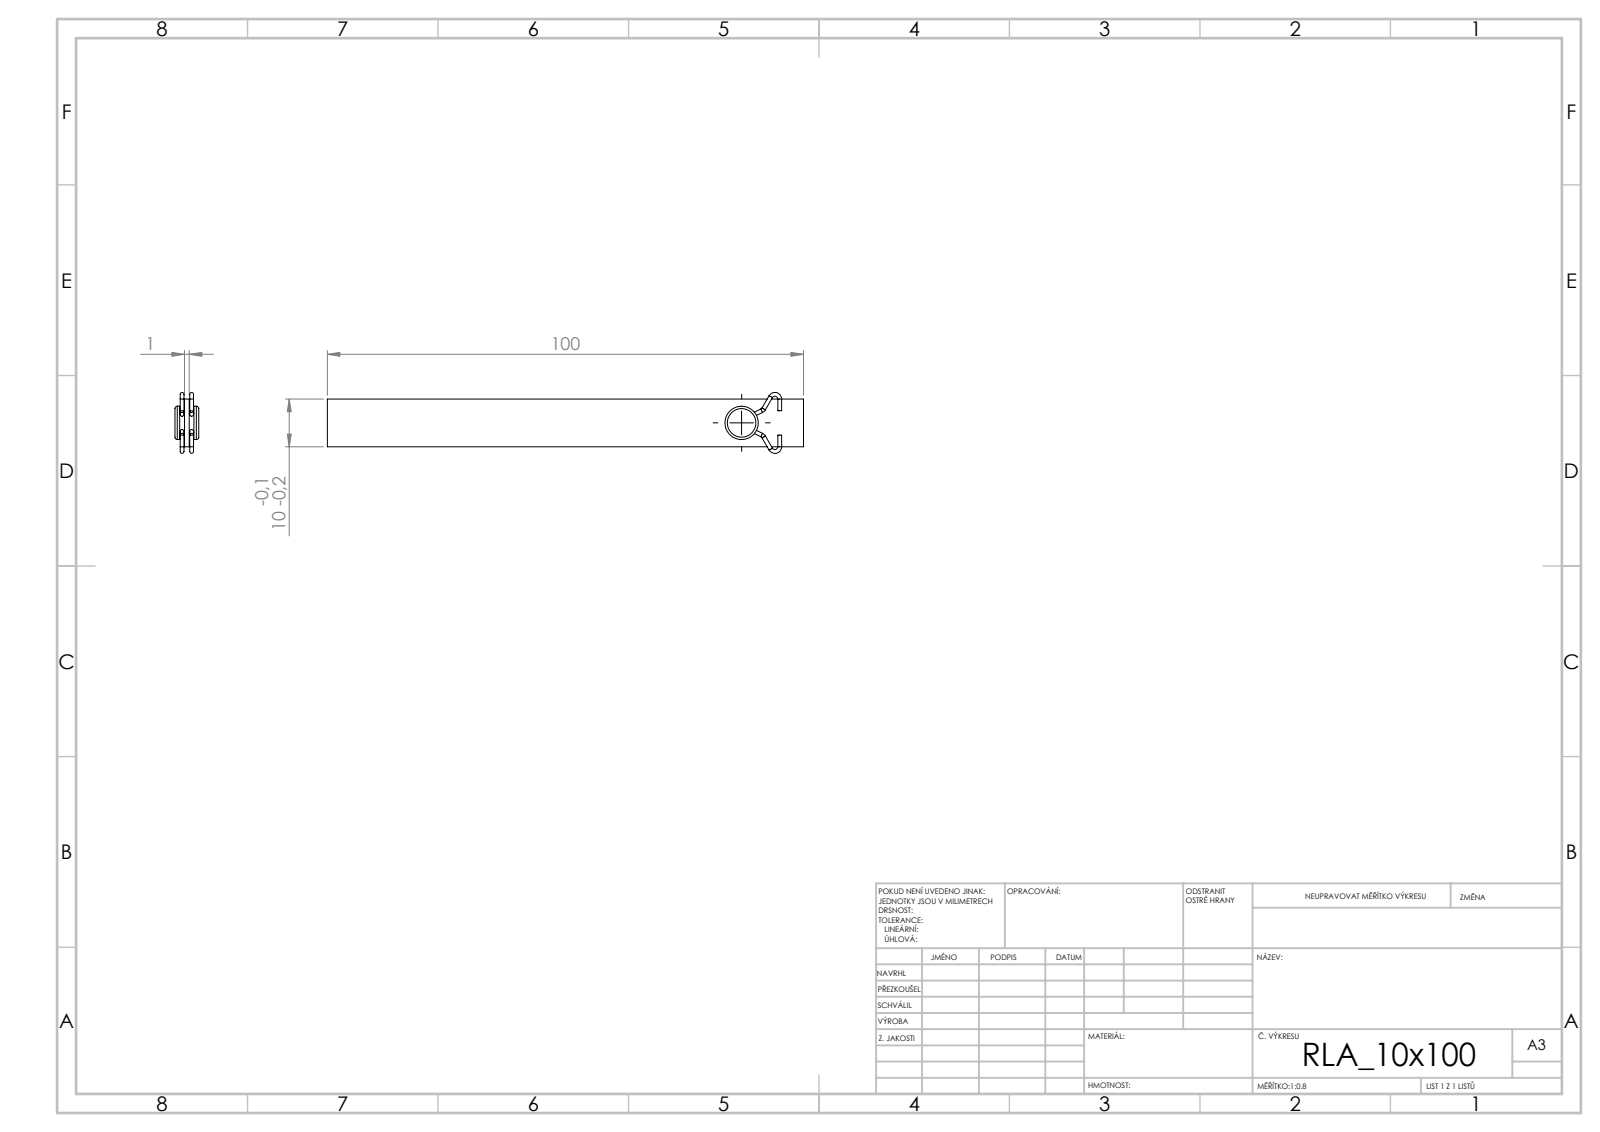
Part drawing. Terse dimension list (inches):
written by: SolidWorks 2019 (CONFIG_CONTROL_DESIGN)
unit: in
bodies: 3 solids, 82 faces (14 planar, 40 cylindrical, 28 other)
size: 3.937 × 0.504 × 0.197
volume: 0.069 in³; area: 3.963 in²
bosses: 14× ⌀0.031, 1× ⌀0.276, 1× ⌀0.157
face distances: 0.039, 0.079, 0.394, 0.118, 0.157, 0.197, 3.937, 0.096, 0.297, 0.201
